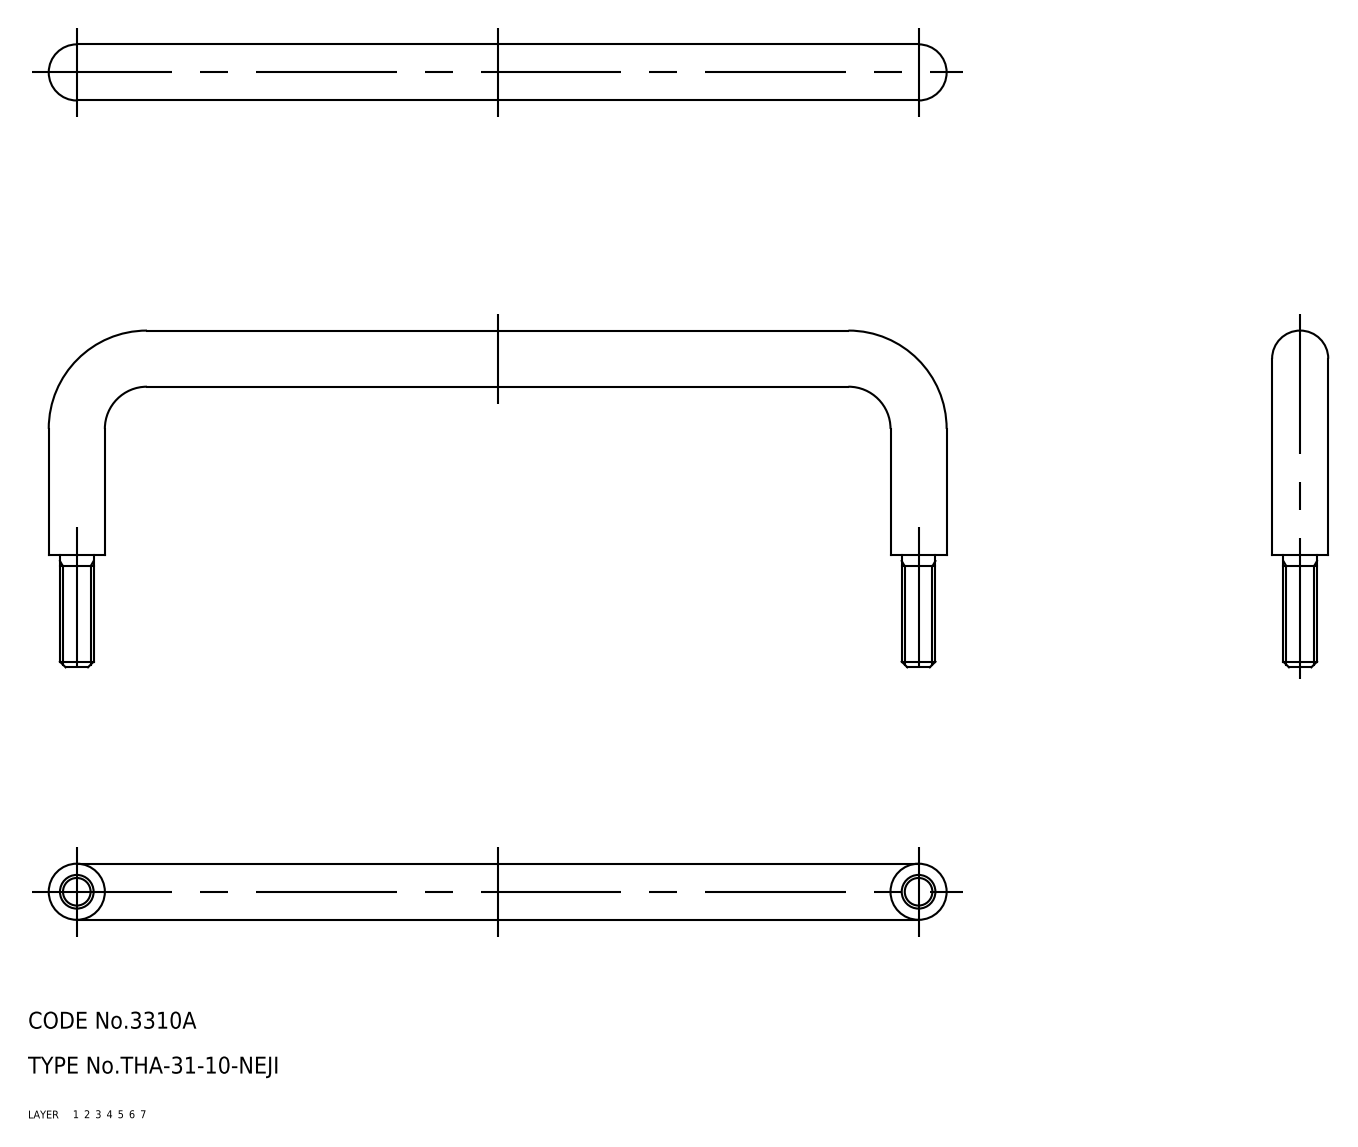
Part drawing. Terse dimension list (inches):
name: pull
written by: CADfix (AUTOMOTIVE_DESIGN)
unit: in
bodies: 1 solid, 22 faces (0 planar, 0 cylindrical, 22 other)
size: 6.299 × 2.362 × 0.394
volume: 1.075 in³; area: 11.57 in²
